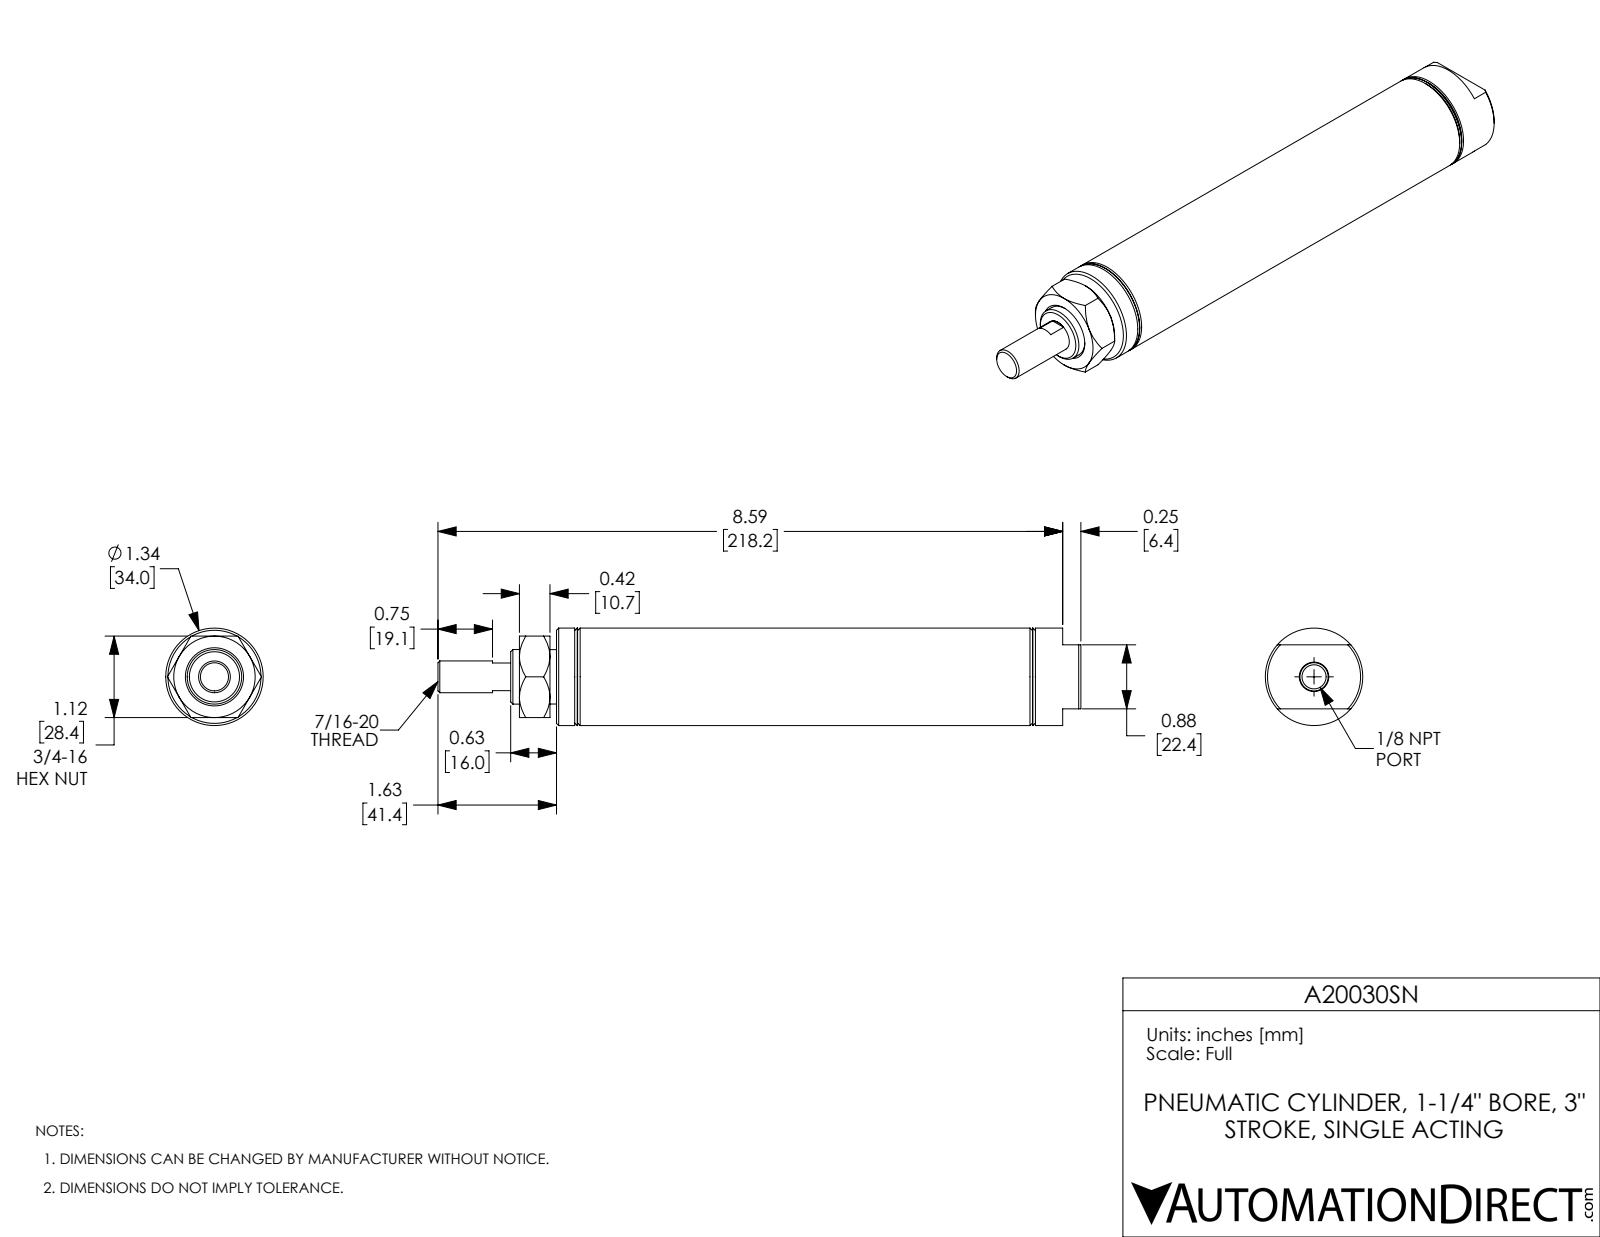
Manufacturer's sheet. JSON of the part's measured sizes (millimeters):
{"part_name": "A20030SN; A20030SN_Mounting Nut_D-3556; A20030SN-Rod; A20030SN-MainBody", "step_written_by": "SolidWorks 2017 (AUTOMOTIVE_DESIGN)", "units": "millimeters", "bodies": {"solids": 3, "faces": 95, "planar": 32, "cylindrical": 26, "other": 37}, "overall_size": [224.5, 34, 34], "volume_mm3": 122600, "surface_area_mm2": 46500, "round_holes": [[8.4, 1], [11.1, 1], [19.1, 1], [31.8, 1]], "round_bosses_or_shafts": [[34, 1], [19, 1]], "face_to_face_distances": [47.1, 136, 88.9, 12.7, 76.2, 59.8, 183.1, 123.3, 28.4, 25.4]}
